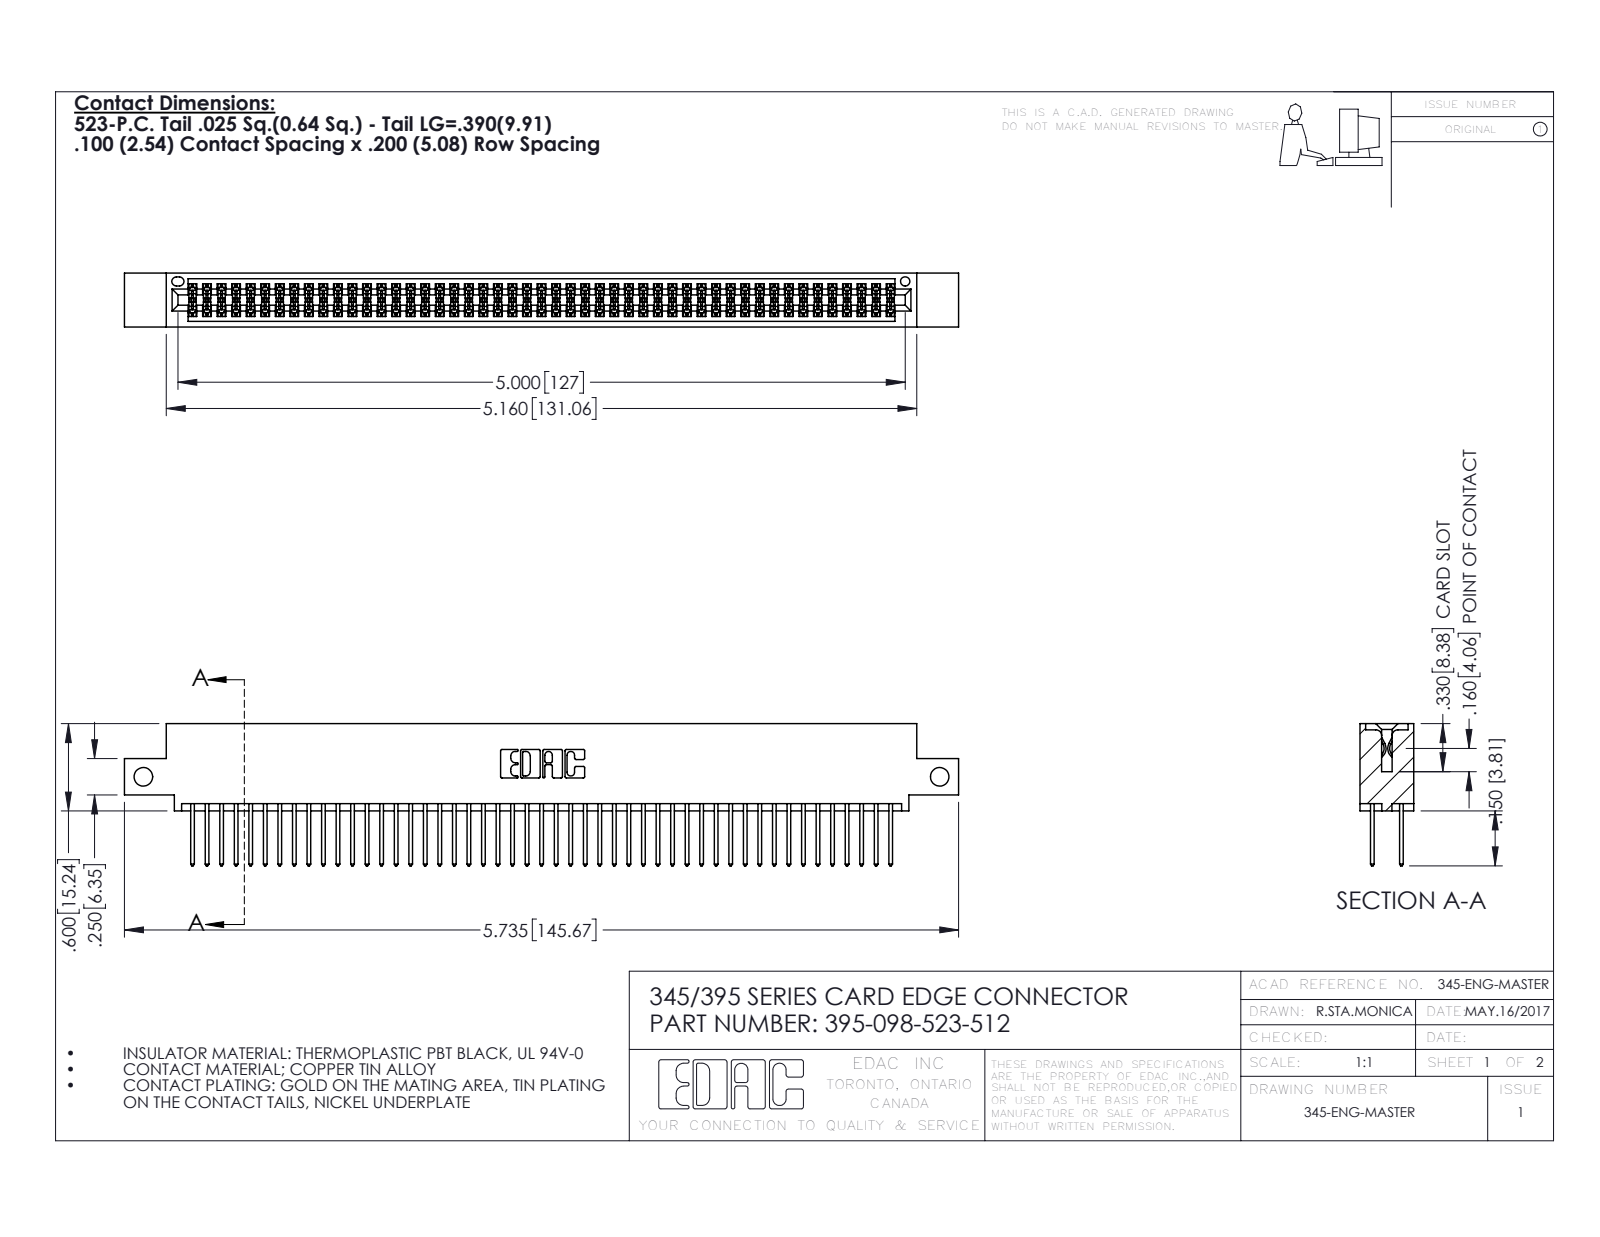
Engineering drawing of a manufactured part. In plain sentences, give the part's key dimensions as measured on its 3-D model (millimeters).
The part is named "345-292-001_345-293-123; 395-098-523-512; 345 Part_0.110 Offset - Side Mount". Its 3-D file was written by "SolidWorks 2016 (CONFIG_CONTROL_DESIGN)". It is 99 solids with 5030 faces: 3318 planar, 1712 cylindrical and 0 other. Overall it measures 145.7 by 24.8 by 9.4 millimeters. Its volume is 14 300 cubic millimeters and its surface area 22 060 square millimeters. Round holes: 2 of diameter 3.3, 1 of diameter 1.6. Partial cylindrical surfaces (rounded edges, fillets, slot ends): 147 of radius 0.2, 98 of radius 0.3, 22 of radius 0.3, 6 of radius 0.2, 6 of radius 0.8, 3 of radius 0.7, 2 of radius 0.4, 2 of radius 0.5. The main face-to-face distances are 7.6, 1.8, 5.1, 2.5, 6.9, 0.6, 9.4, 5.7, 4.4, 3.8. The hole center spacings are 139.1.
